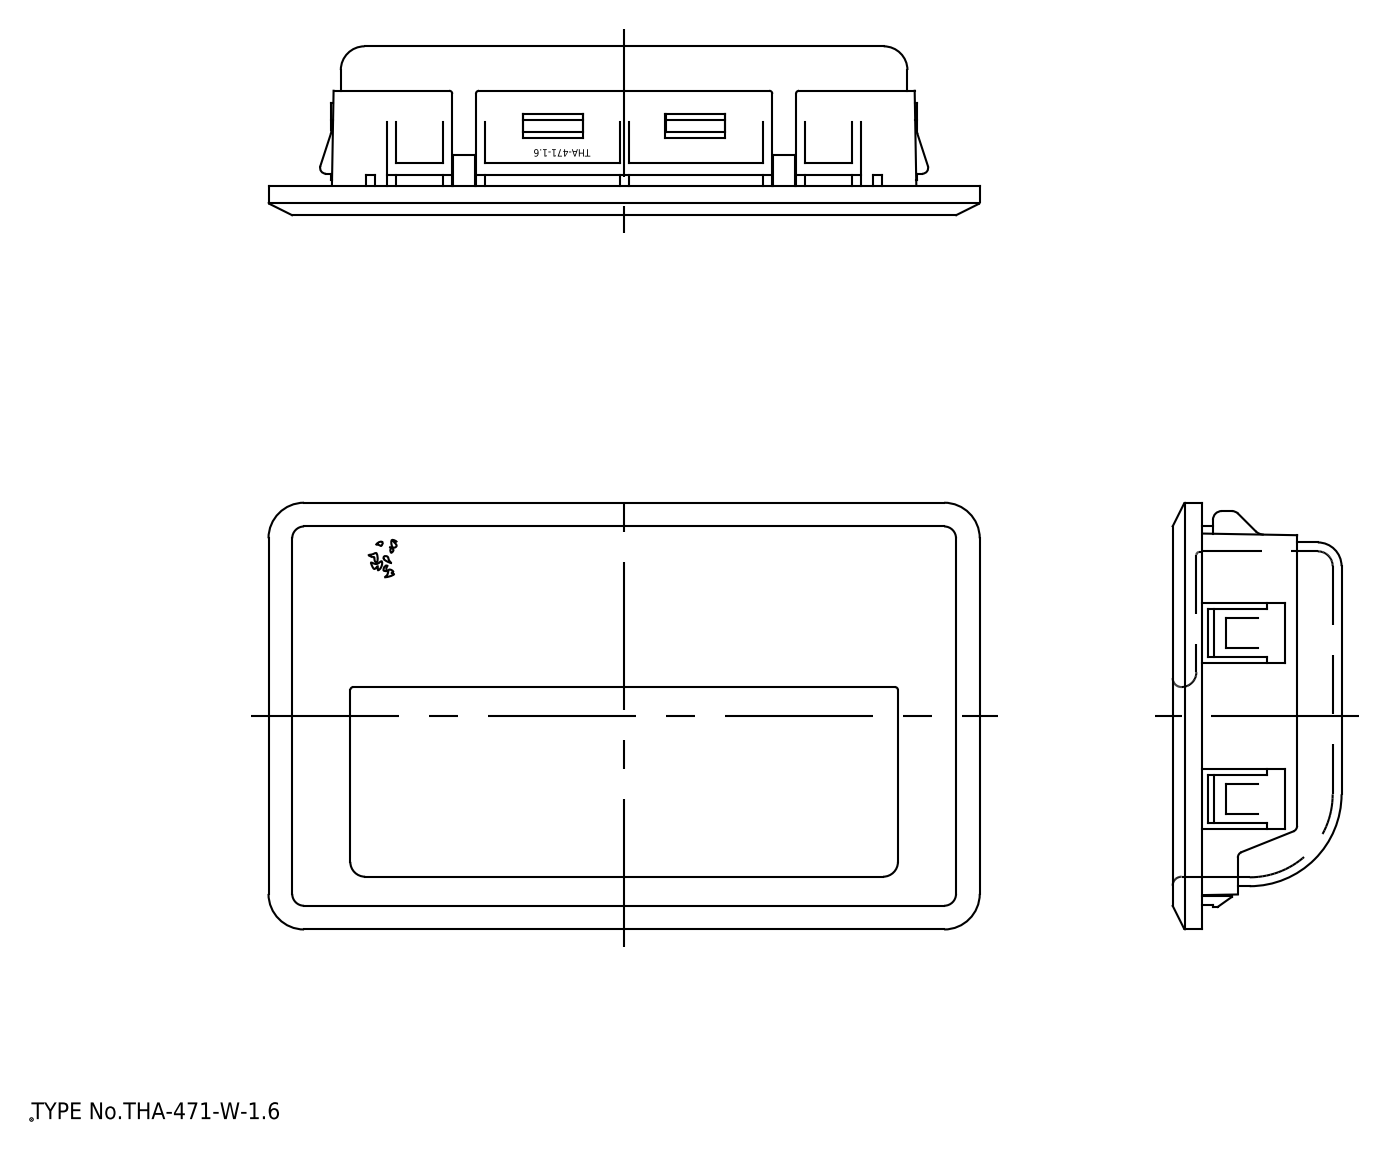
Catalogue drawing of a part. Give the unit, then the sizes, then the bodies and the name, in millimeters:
Units: millimetres
Overall size (bounding box): 120 × 72 × 28.5
Partial cylindrical surfaces — rounded edges, fillets, slot ends (radius × count): R0.5 ×137, R4 ×17, R2.5 ×10, R0.3 ×8, R2 ×7, R1.5 ×6, R1 ×4, R3 ×4
Main face-to-face distances: 1.5, 28.5, 27, 5, 22, 23.5, 2, 94.1, 3, 56.5
Volume: 41 637 mm³ · Surface area: 45 723 mm²
Bodies: 1 solid, 975 faces (428 planar, 355 cylindrical, 192 other)
STEP written by: spGate 16.7.1 (AUTOMOTIVE_DESIGN)
